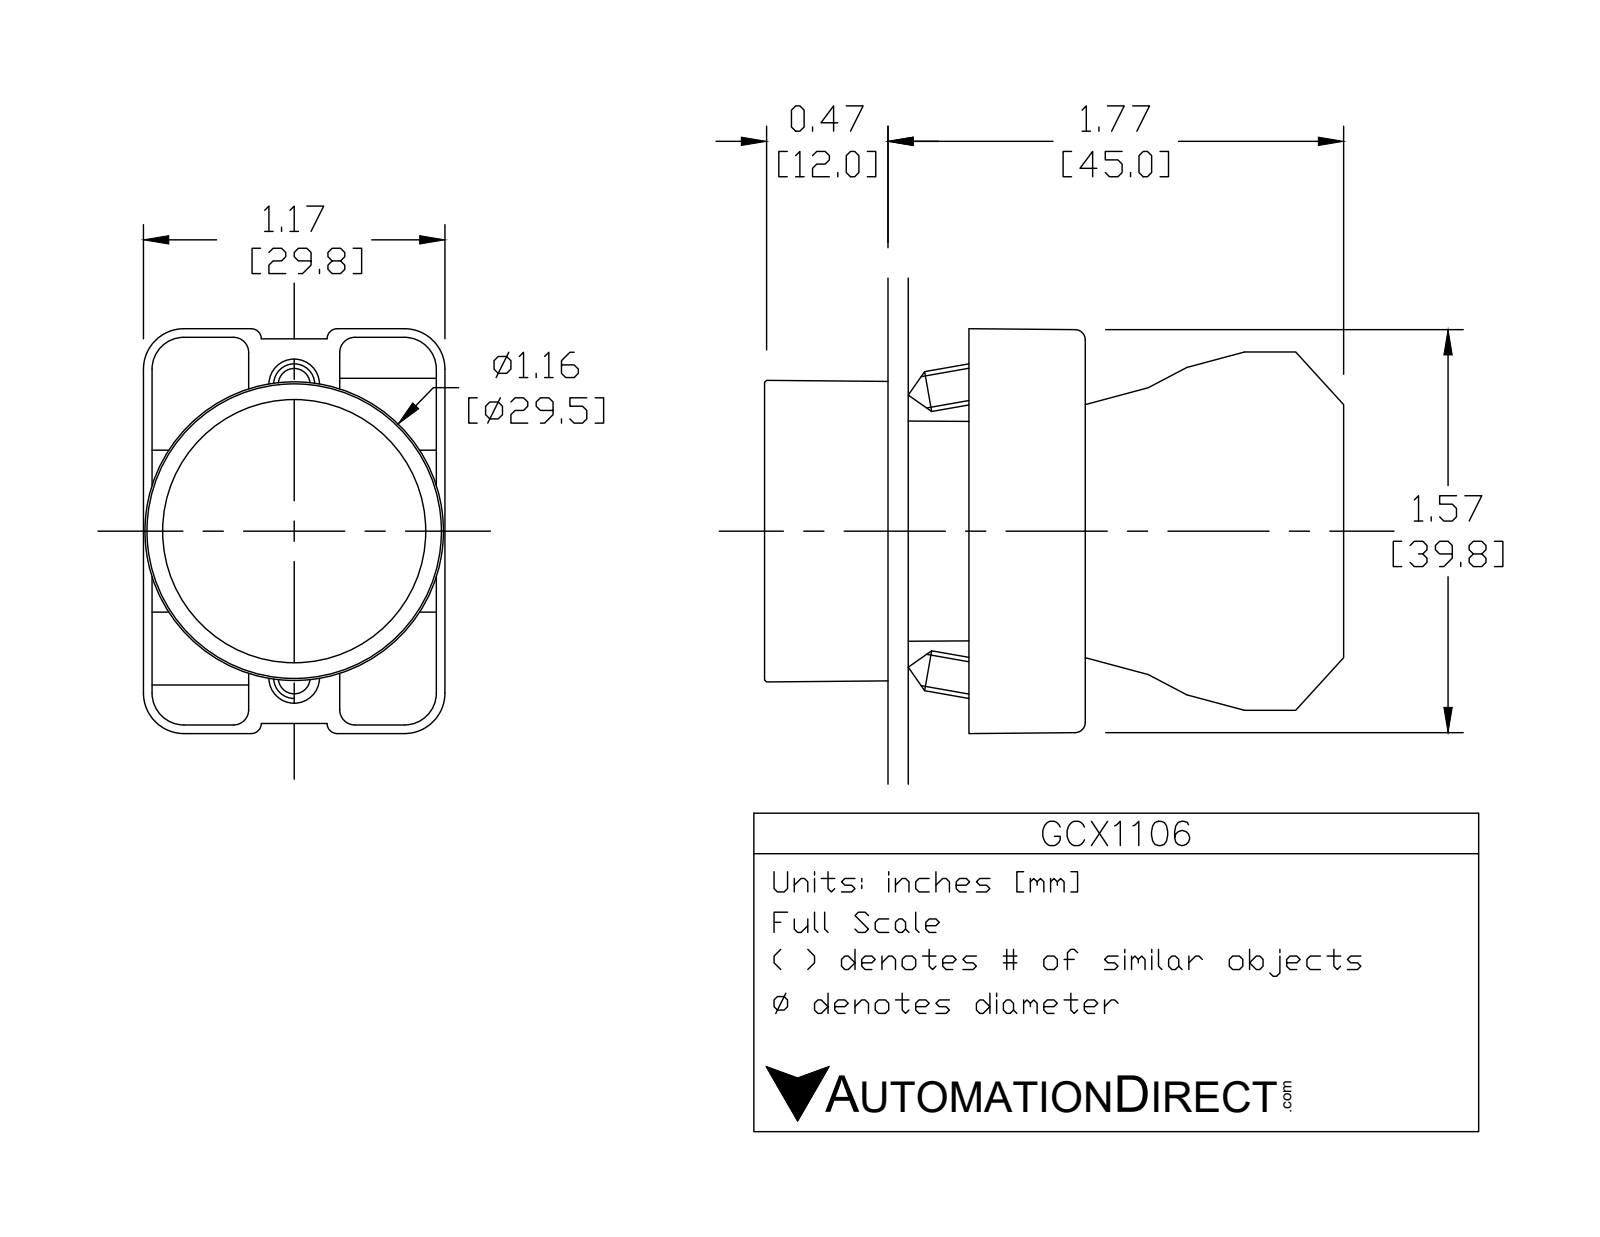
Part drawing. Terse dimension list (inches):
name: GCX1106; GCX1106 OPERATOR; ecx1029; ecx1040
written by: SolidWorks 2016 (AUTOMOTIVE_DESIGN)
unit: in
bodies: 6 solids, 387 faces (224 planar, 136 cylindrical, 27 other)
size: 2.217 × 1.581 × 1.177
volume: 1.741 in³; area: 27.14 in²
holes: 2× ⌀0.079, 2× ⌀0.124, 2× ⌀0.13, 1× ⌀0.087, 1× ⌀0.197, 1× ⌀0.709, 1× ⌀0.878, 1× ⌀0.888, 1× ⌀1.024
bosses: 2× ⌀0.157, 1× ⌀1.175, 1× ⌀1.004, 1× ⌀0.945, 1× ⌀0.856, 1× ⌀0.78, 1× ⌀0.551
rounds: 24× R0.059, 12× R0.041, 12× R0.124, 12× R0.157, 4× R0.039, 2× R0.128, 1× R0.02, 1× R0.063
face distances: 0.72, 0.579, 0.033, 0.472, 1.193, 0.031, 0.689, 0.598, 1.161, 1.071
hole spacings: 0.236, 0.544, 0.472, 0.49
